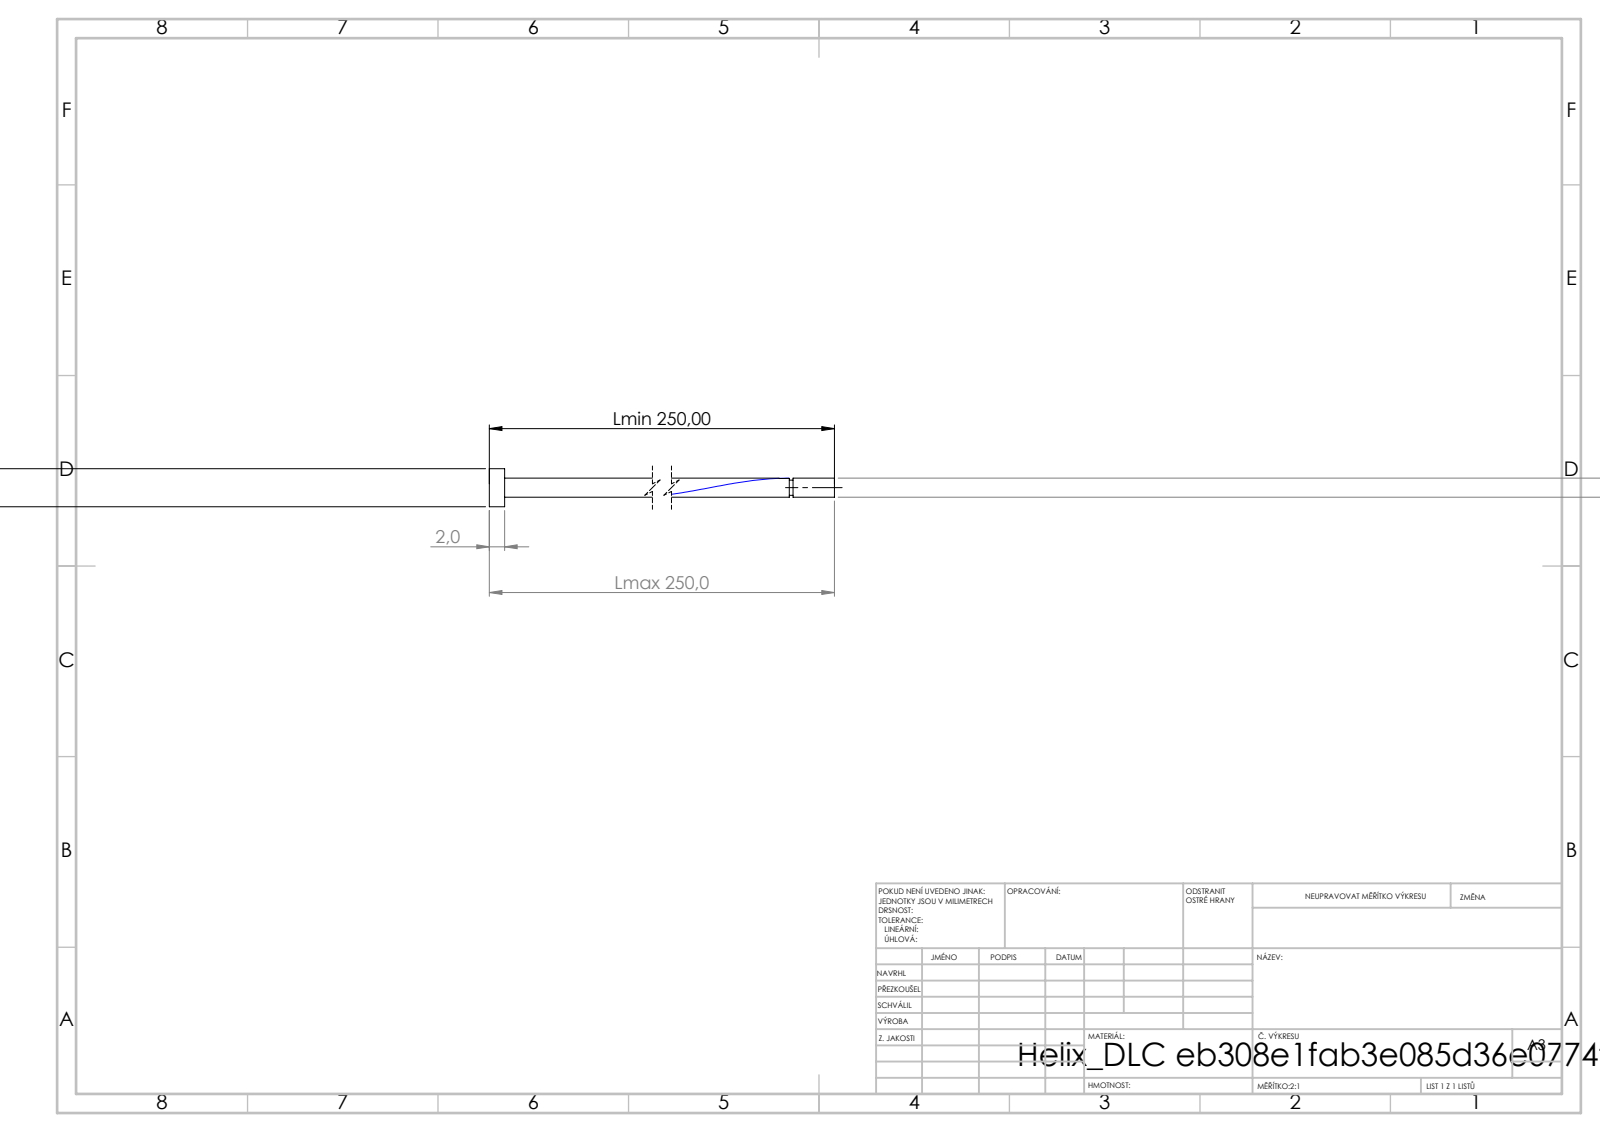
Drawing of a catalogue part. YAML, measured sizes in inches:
step_written_by: "SolidWorks 2019 (CONFIG_CONTROL_DESIGN)"
units: inches
bodies: {solids: 1, faces: 16, planar: 6, cylindrical: 9, other: 1}
overall_size: [9.843, 0.197, 0.197]
volume: 0.093
surface_area: 4.194
round_bosses_or_shafts:
  - {diameter: 0.197, count: 1}
  - {diameter: 0.098, count: 1}
  - {diameter: 0.079, count: 1}
face_to_face_distances: [0.079, 9.843, 9.764, 9.629, 9.55, 0.214, 9.609, 9.53, 0.02, 0.233]
